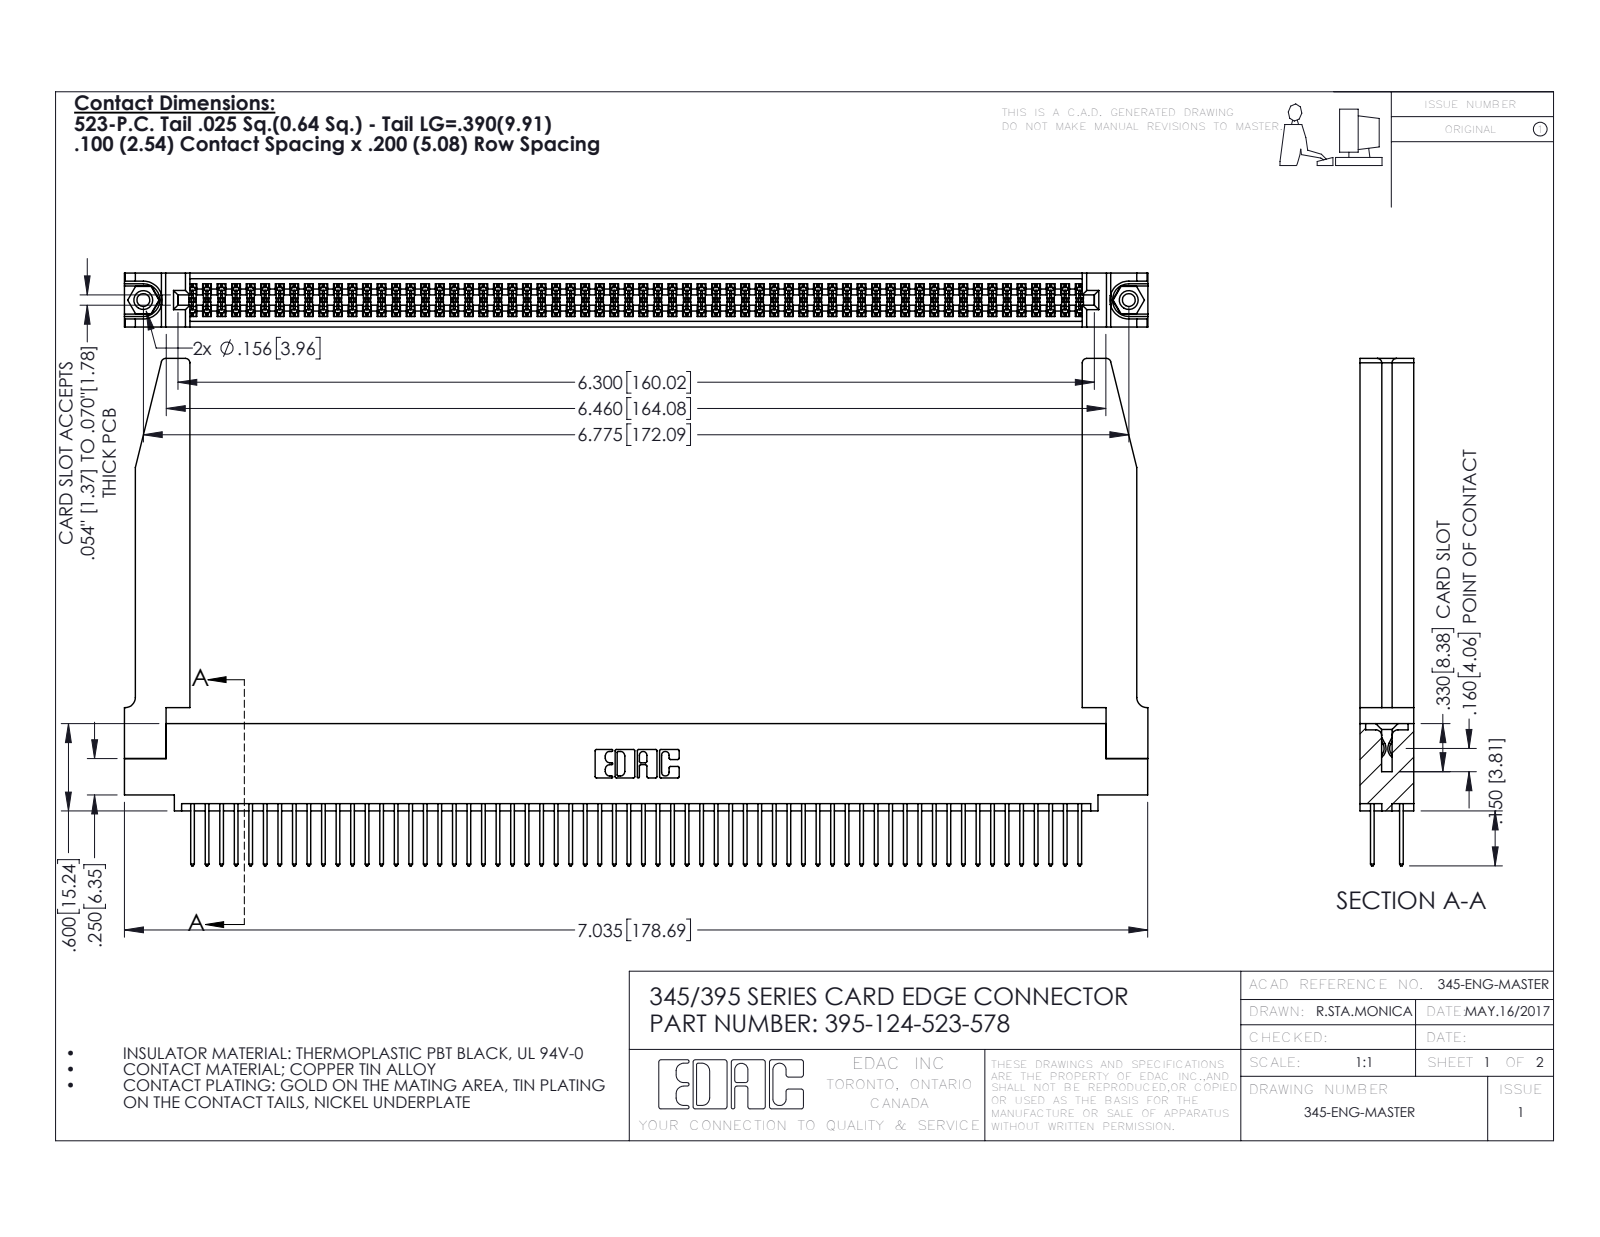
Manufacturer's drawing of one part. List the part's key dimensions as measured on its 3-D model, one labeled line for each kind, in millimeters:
Part name (STEP PRODUCT): 345-292-001_345-293-123; 345 Part_0.110 Offset - 0.156 Dia-TH; 345-250-001_345-250-001-102; 395-124-523-578 (+1 more)
STEP written by: SolidWorks 2016 (CONFIG_CONTROL_DESIGN)
Units: millimetres
Bodies: 129 solids, 6564 faces (4318 planar, 2194 cylindrical, 52 other)
Overall size (bounding box): 178.7 × 88.6 × 9.4
Volume: 25 500 mm³ · Surface area: 34 660 mm²
Round holes (diameter × count): ⌀2.3 ×2, ⌀3.2 ×2, ⌀4 ×2, ⌀1.6 ×1
Round bosses / shafts (diameter × count): ⌀3.9 ×2
Partial cylindrical surfaces — rounded edges, fillets, slot ends (radius × count): R0.2 ×186, R0.3 ×124, R0.3 ×22, R0.8 ×8, R0.2 ×6, R0.8 ×6, R0.7 ×3, R0.4 ×2
Main face-to-face distances: 1.8, 7.6, 9.4, 2.5, 6.9, 0.6, 5.1, 5.7, 4.4, 3.8
Hole centre spacings: 6.9, 166.1, 172.1
